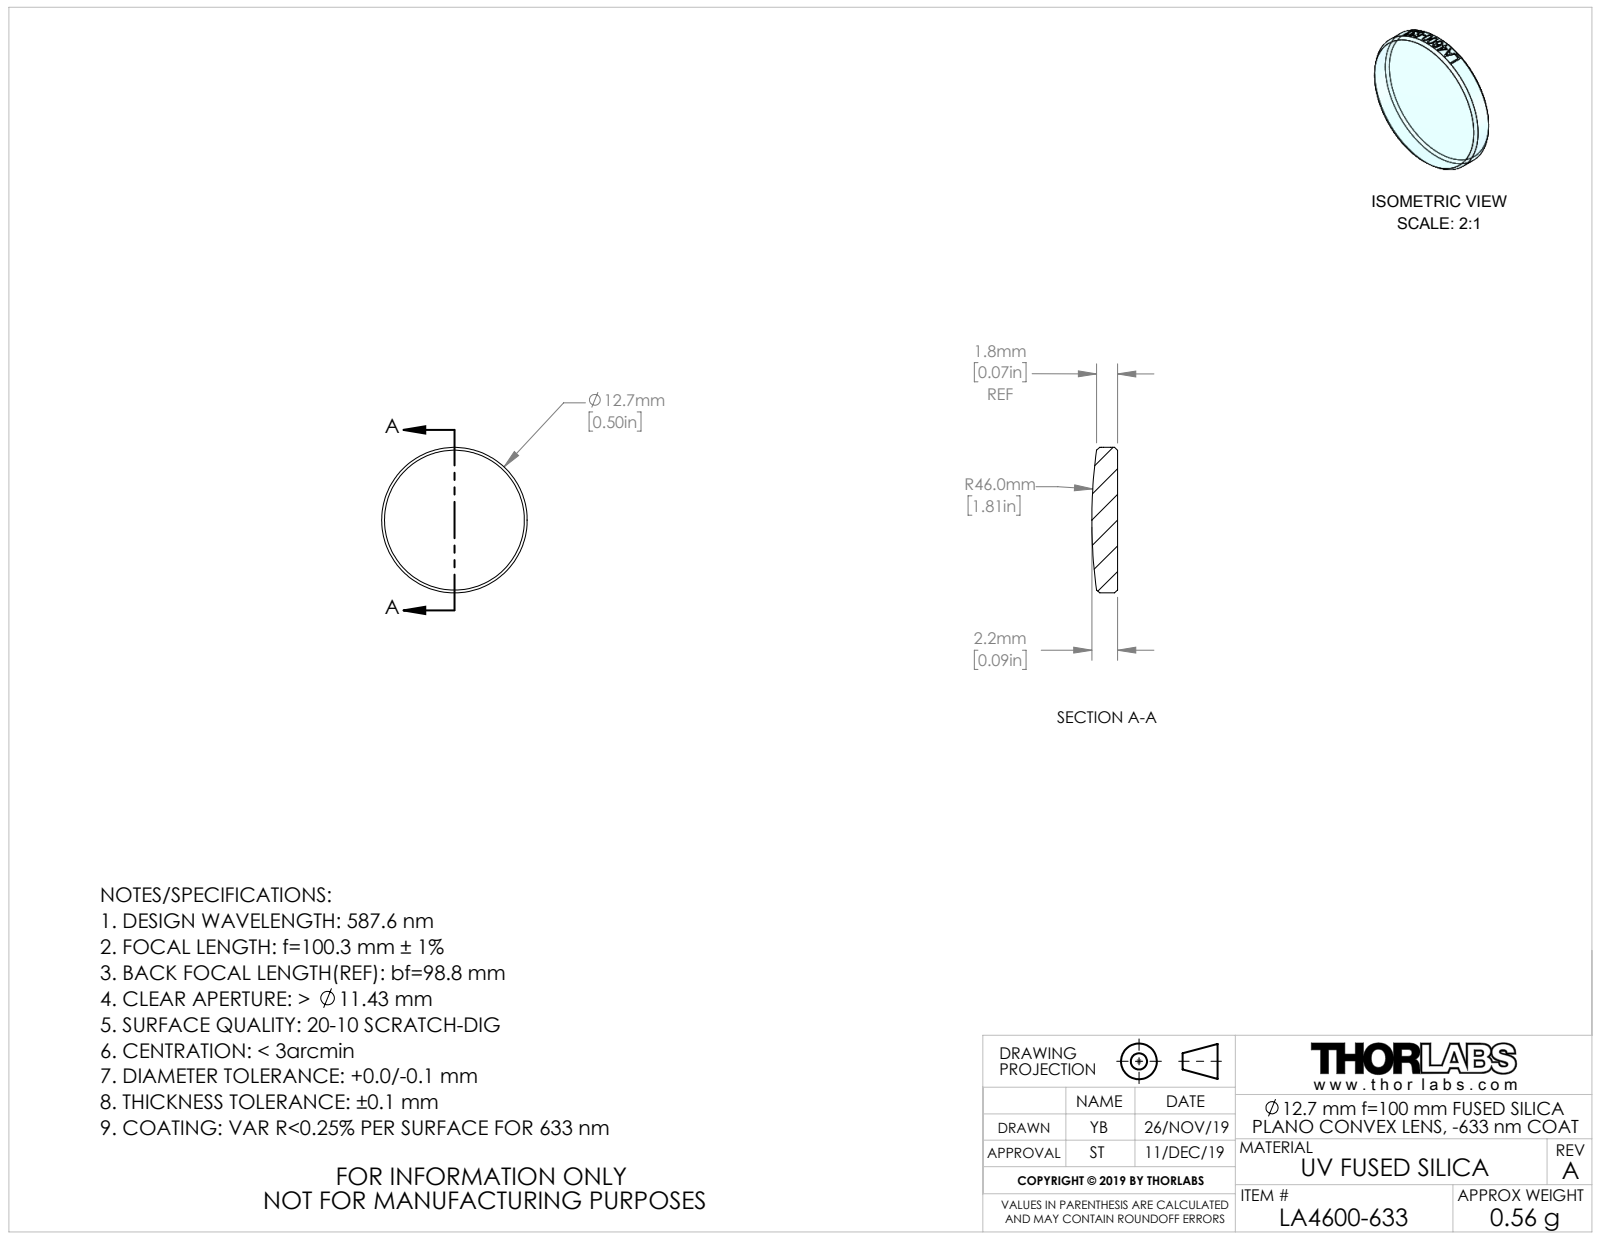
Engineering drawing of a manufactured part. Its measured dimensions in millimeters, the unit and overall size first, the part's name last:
Units: millimetres
Overall size (bounding box): 12.7 × 12.7 × 2.24
Round bosses / shafts (diameter × count): ⌀12.7 ×1
Volume: 254 mm³ · Surface area: 315 mm²
Bodies: 1 solid, 25 faces (1 planar, 18 cylindrical, 6 other)
Part name (STEP PRODUCT): CTN014990-999; CTN015009
STEP written by: SolidWorks 2018 (AUTOMOTIVE_DESIGN)
